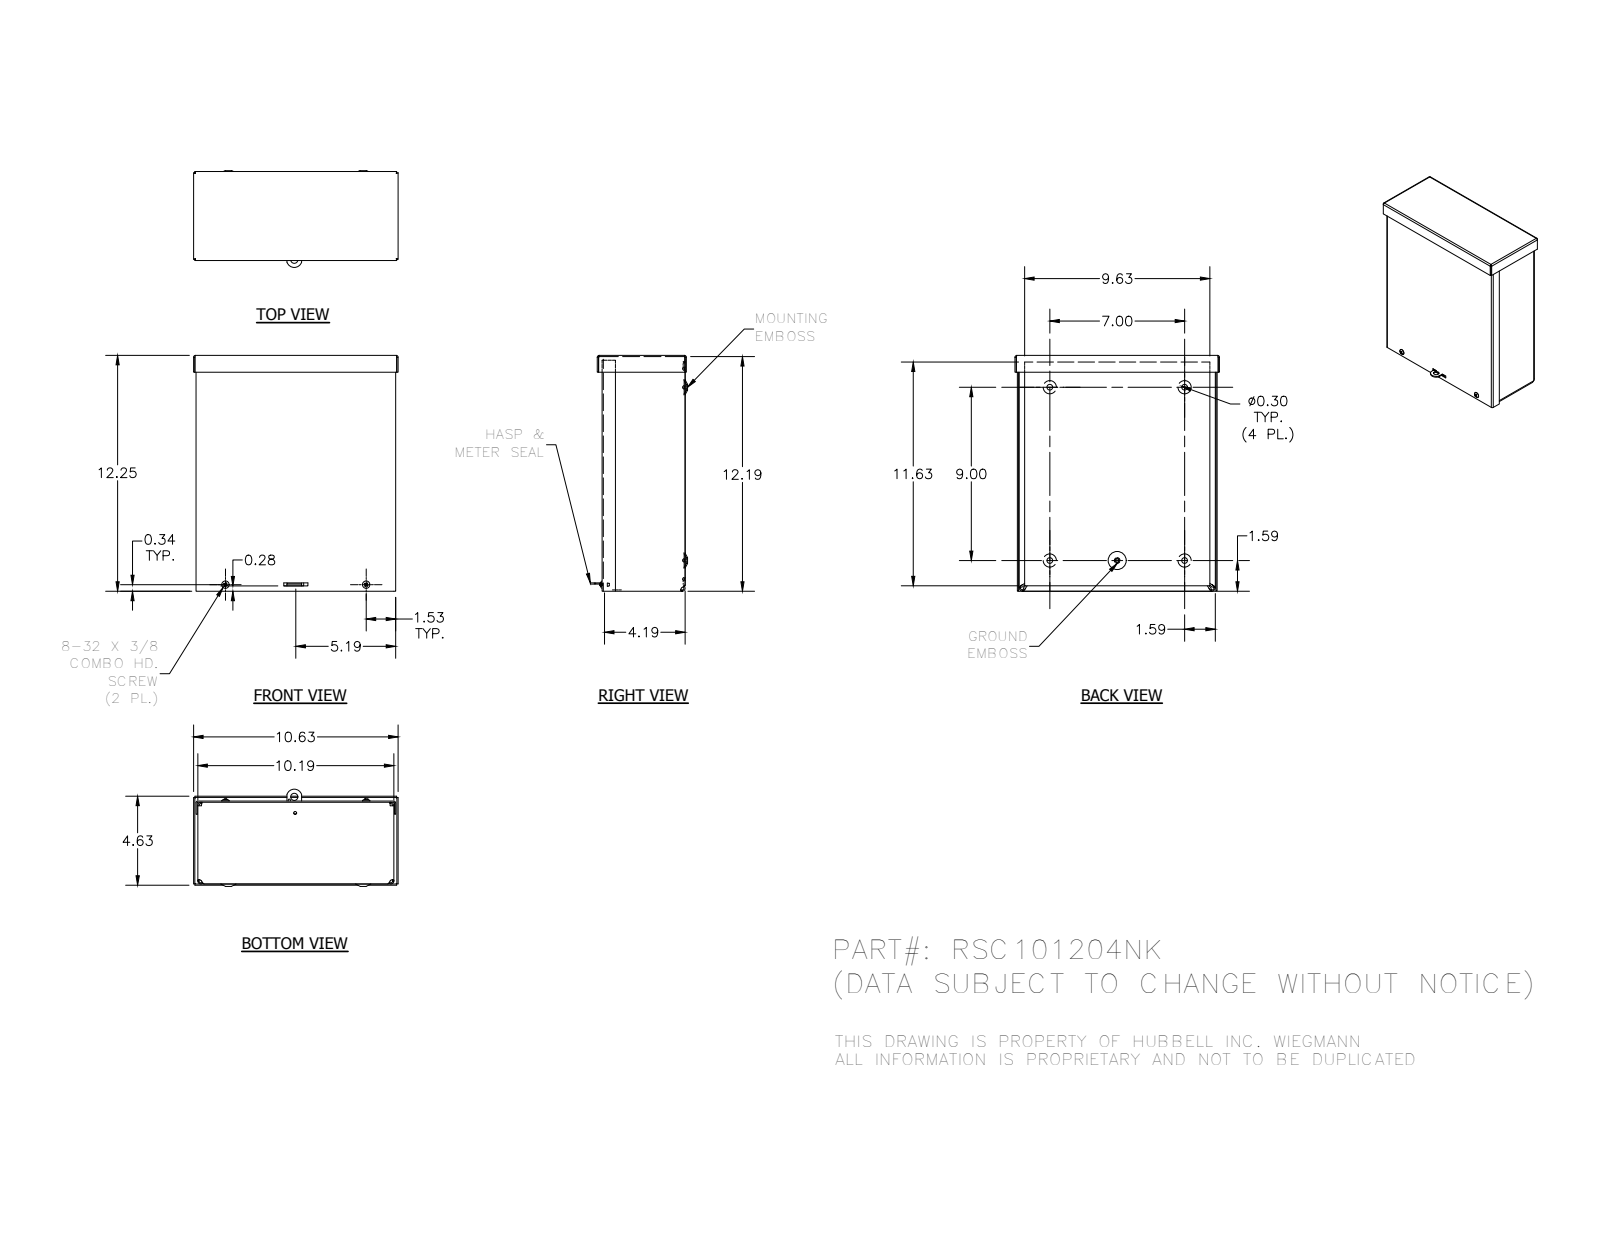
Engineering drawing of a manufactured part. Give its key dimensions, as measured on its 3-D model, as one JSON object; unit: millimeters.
{"part_name": "RSC101204NK_WRAP; RSC1012NK_LID; RSC1004NK_CAP; 3183 (+3 more)", "step_written_by": "Autodesk Inventor 2014 (AUTOMOTIVE_DESIGN)", "units": "millimeters", "bodies": {"solids": 7, "faces": 377, "planar": 163, "cylindrical": 78, "other": 136}, "overall_size": [311.16, 269.88, 130.17], "volume_mm3": 580626, "surface_area_mm2": 746883, "round_holes": [[7.62, 4], [7.95, 4], [3.76, 2], [3.17, 1], [3.45, 1], [3.96, 1], [4.19, 1], [9.52, 1]], "round_bosses_or_shafts": [[9.75, 2], [4.17, 2], [5.8, 1]], "partial_cylinders_radius": [[0.79, 8], [2.37, 8], [3.17, 8], [4.75, 8], [1.4, 4], [1.57, 4], [2.38, 4], [2.97, 4]], "face_to_face_distances": [1.58, 107.93, 1.57, 106.35, 1.59, 109.52, 107.94, 257.19, 307.99, 3.15], "hole_center_spacings": [27.24, 32.03, 88.9, 177.8, 185.75, 228.6, 245.27, 255.58]}
